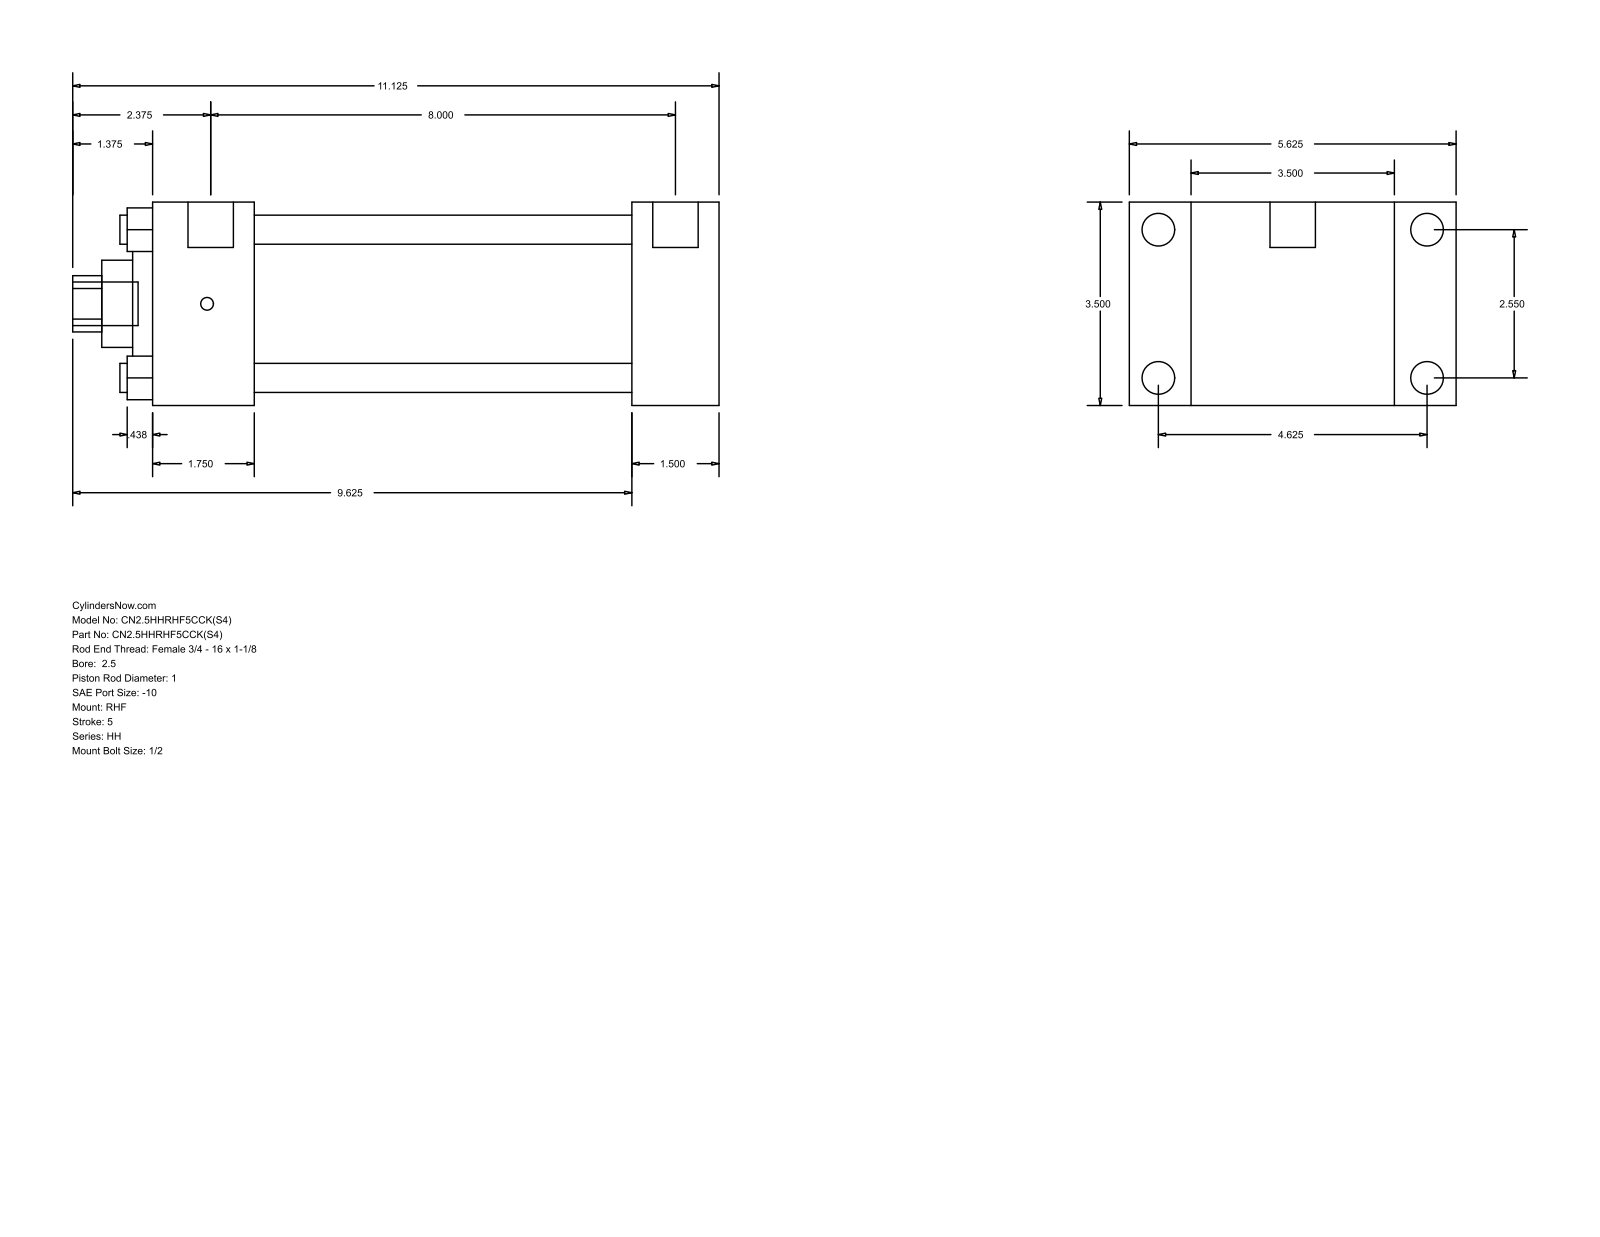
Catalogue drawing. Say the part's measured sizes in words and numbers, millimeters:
The part is named "HH_RHF__0250_1". Its 3-D file was written by "GSSL Pune (CONFIG_CONTROL_DESIGN)". It is 0 solids with 90 faces: 61 planar, 29 cylindrical and 0 other. Overall it measures 282.57 by 142.88 by 88.9 millimeters. Round holes: 4 of diameter 12.7, 1 of diameter 25.4, 1 of diameter 38.1, 1 of diameter 60.33, 1 of diameter 73.03. Round bosses or shafts: 4 of diameter 14.3, 4 of diameter 5.56, 2 of diameter 19.84, 1 of diameter 19.05. Partial cylindrical surfaces (rounded edges, fillets, slot ends): 1 of radius 12.29. The main face-to-face distances are 88.9, 38.1, 26.99, 115.89, 209.55, 247.65, 142.88, 44.46, 165.09, 203.19. The hole center spacings are 45.79, 64.76, 91.58.
